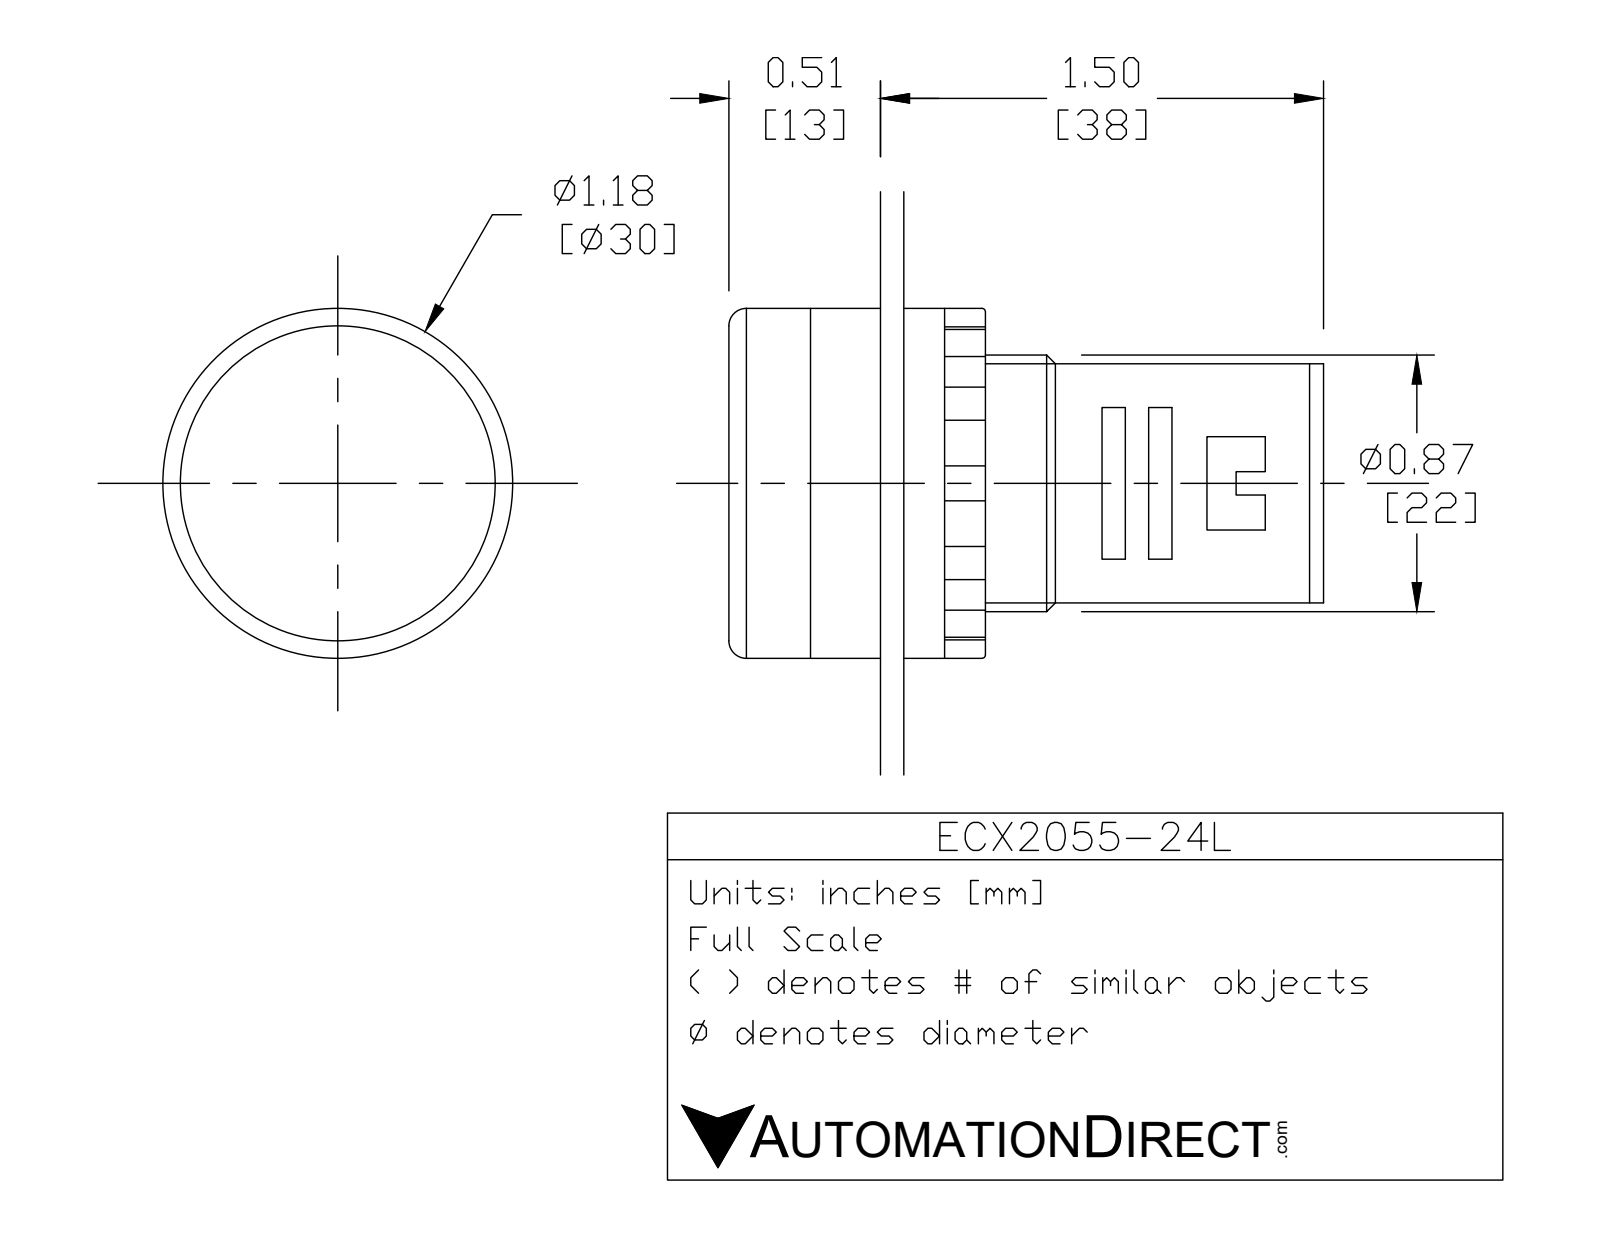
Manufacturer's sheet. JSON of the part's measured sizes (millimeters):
{"part_name": "ECX2055-24L", "step_written_by": "SolidWorks 2017 (AUTOMOTIVE_DESIGN)", "units": "millimeters", "bodies": {"solids": 6, "faces": 123, "planar": 63, "cylindrical": 39, "other": 21}, "overall_size": [51, 30, 30], "volume_mm3": 22483, "surface_area_mm2": 9831, "round_holes": [[5.5, 2], [22.5, 1]], "round_bosses_or_shafts": [[4, 2], [30, 1], [29, 1], [26.5, 1], [22, 1], [20, 1]], "partial_cylinders_radius": [[1, 12]], "face_to_face_distances": [6, 19, 13, 7, 2, 25, 4, 12, 17, 15], "hole_center_spacings": [4.62, 9.24]}
